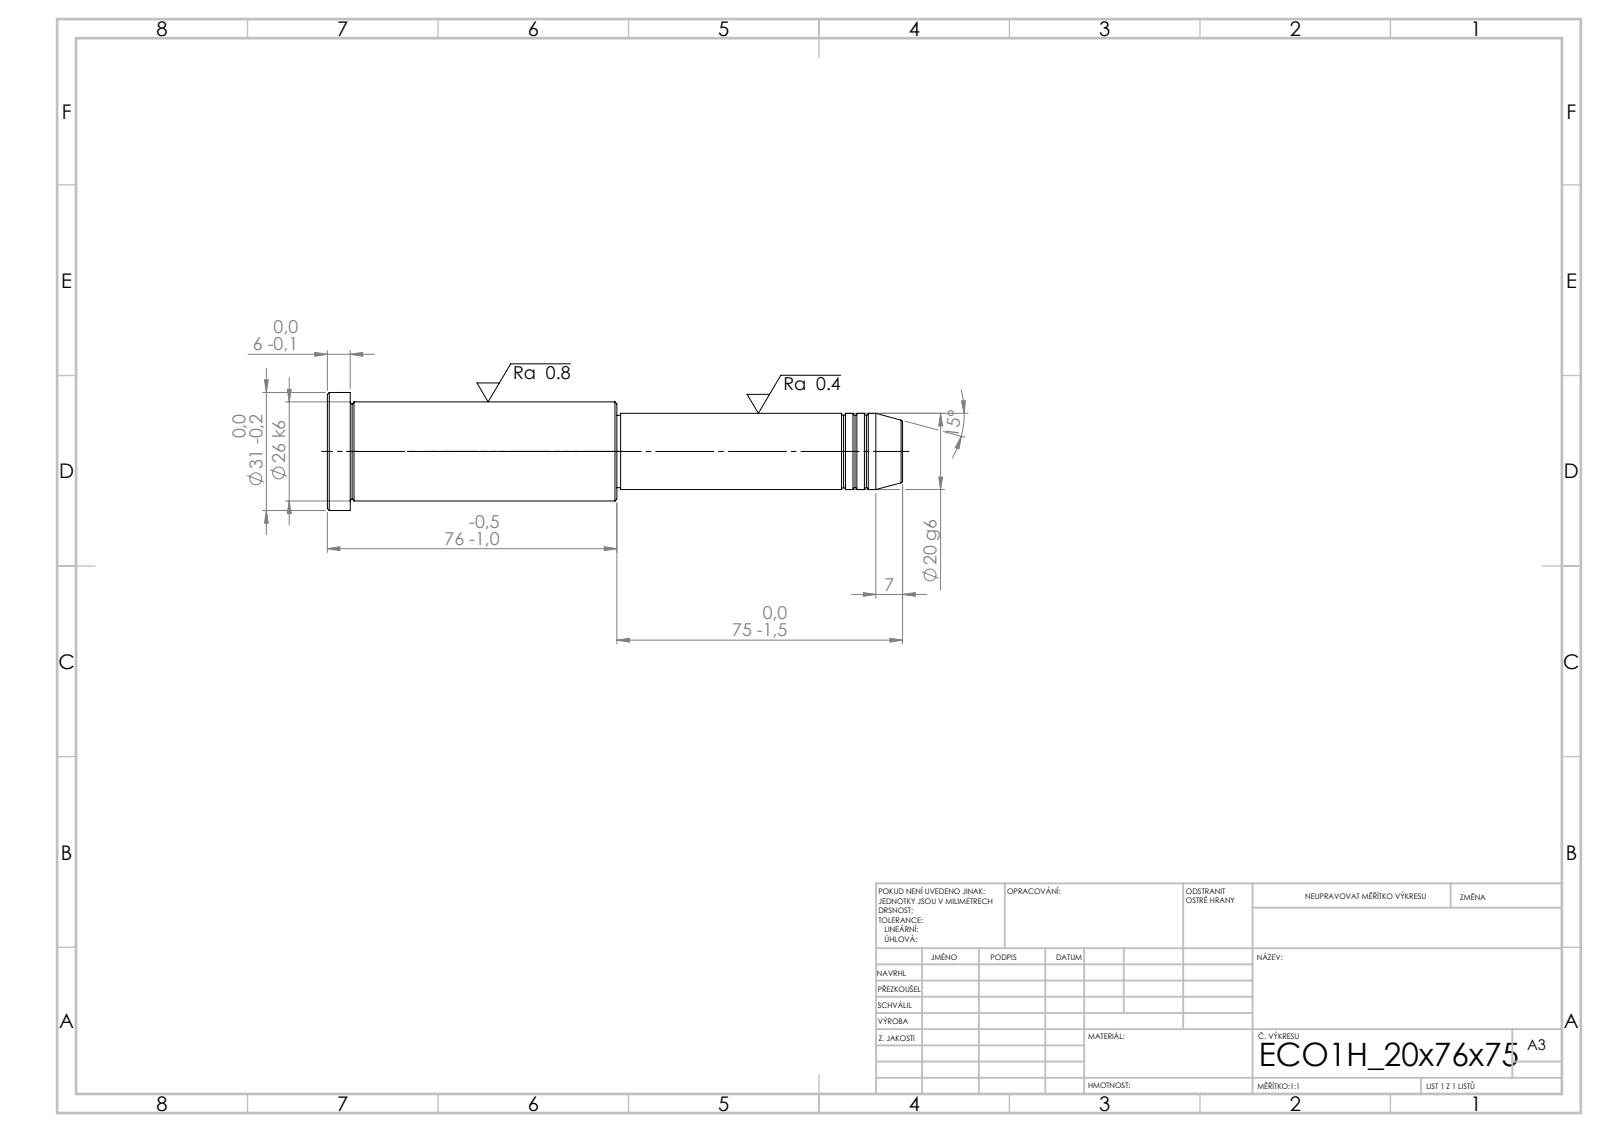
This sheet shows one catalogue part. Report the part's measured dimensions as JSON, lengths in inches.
{"step_written_by": "SolidWorks 2019 (CONFIG_CONTROL_DESIGN)", "units": "inches", "bodies": {"solids": 1, "faces": 43, "planar": 5, "cylindrical": 14, "other": 24}, "overall_size": [5.945, 1.22, 1.22], "volume_in3": 3.949, "surface_area_in2": 19.42, "round_bosses_or_shafts": [[1.22, 1], [1.024, 1], [0.787, 1], [0.748, 1]], "face_to_face_distances": [0.236, 2.756, 2.992, 2.953, 5.709, 5.945, 2.913, 0.039, 2.795, 3.031]}
